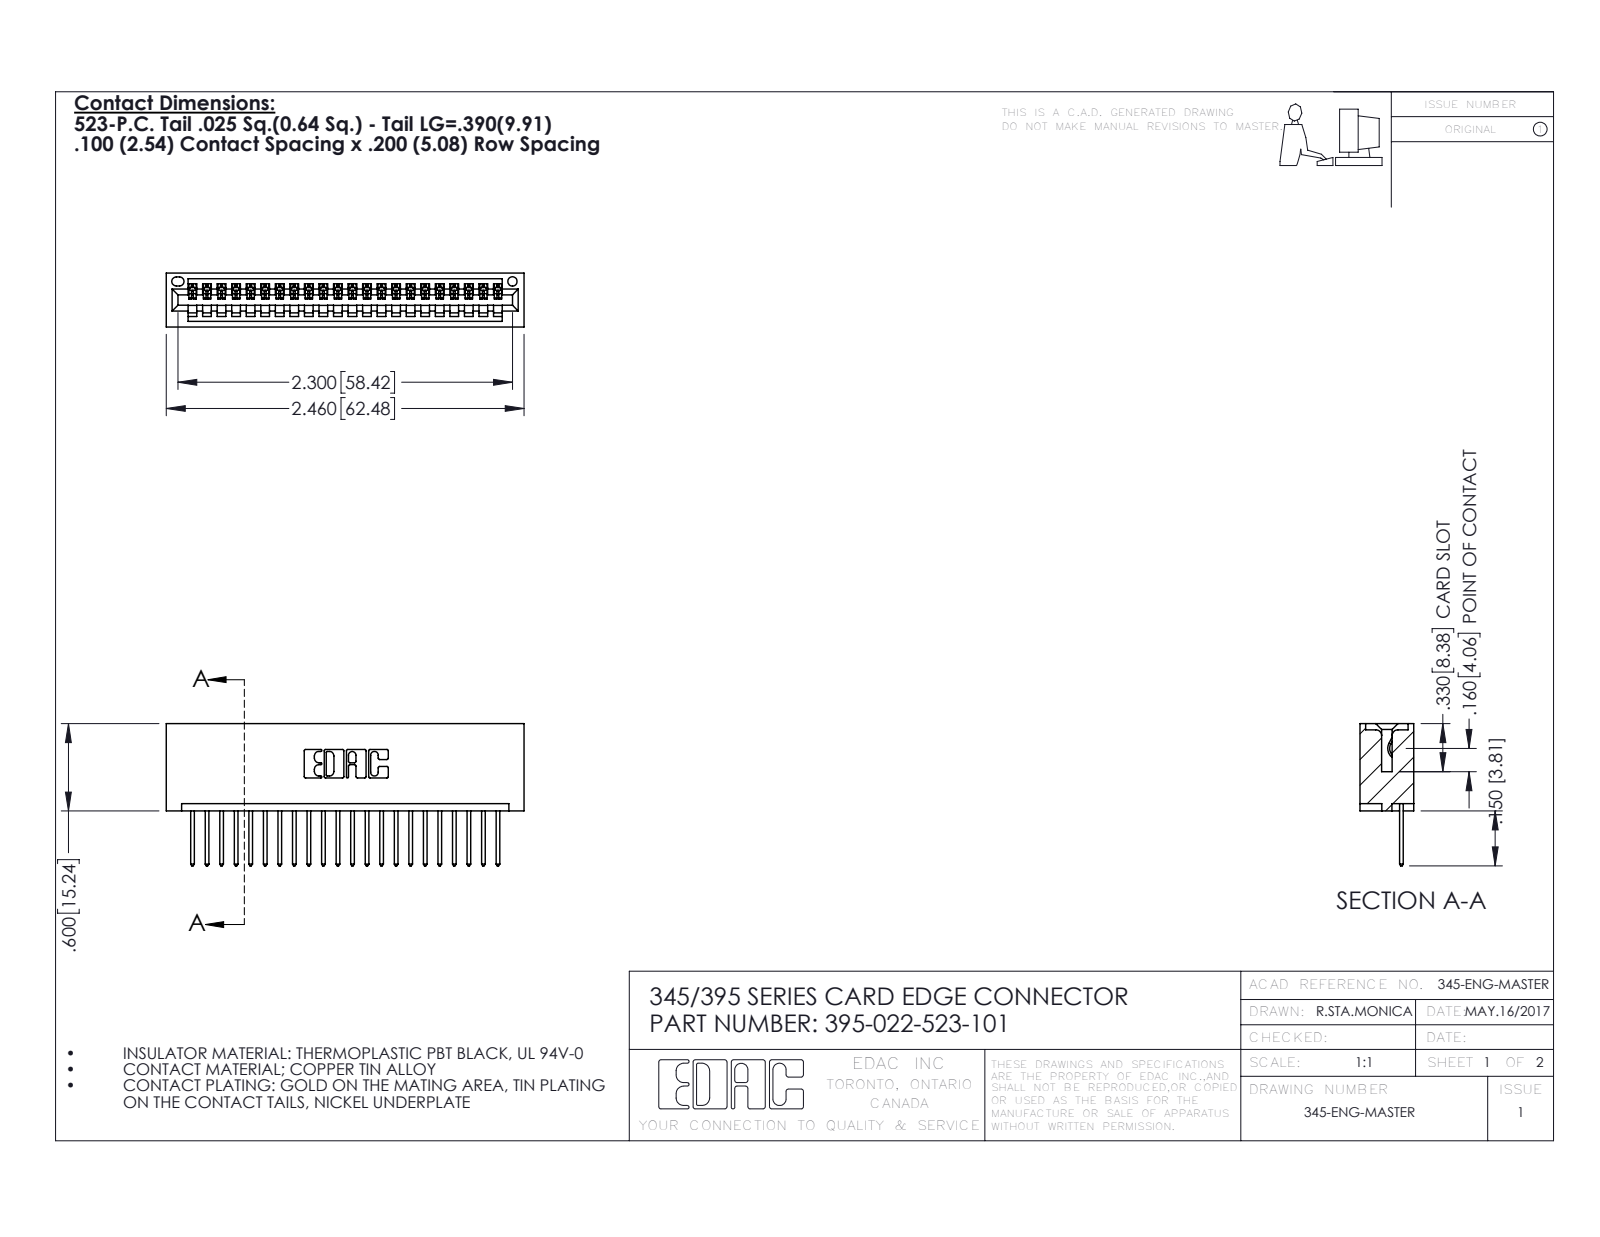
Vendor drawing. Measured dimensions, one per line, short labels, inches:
name: 345-292-001_345-293-123; 345 Part_No Mounting Lugs; 395-022-523-101
written by: SolidWorks 2016 (CONFIG_CONTROL_DESIGN)
unit: in
bodies: 23 solids, 1394 faces (956 planar, 438 cylindrical, 0 other)
size: 2.46 × 0.977 × 0.37
volume: 0.387 in³; area: 12.98 in²
holes: 1× ⌀0.064
rounds: 44× R0.006, 44× R0.01, 22× R0.01, 6× R0.007, 6× R0.031, 3× R0.026, 2× R0.031, 2× R0.04
face distances: 0.298, 0.072, 0.2, 0.37, 0.098, 0.272, 0.025, 0.225, 0.1, 0.149
